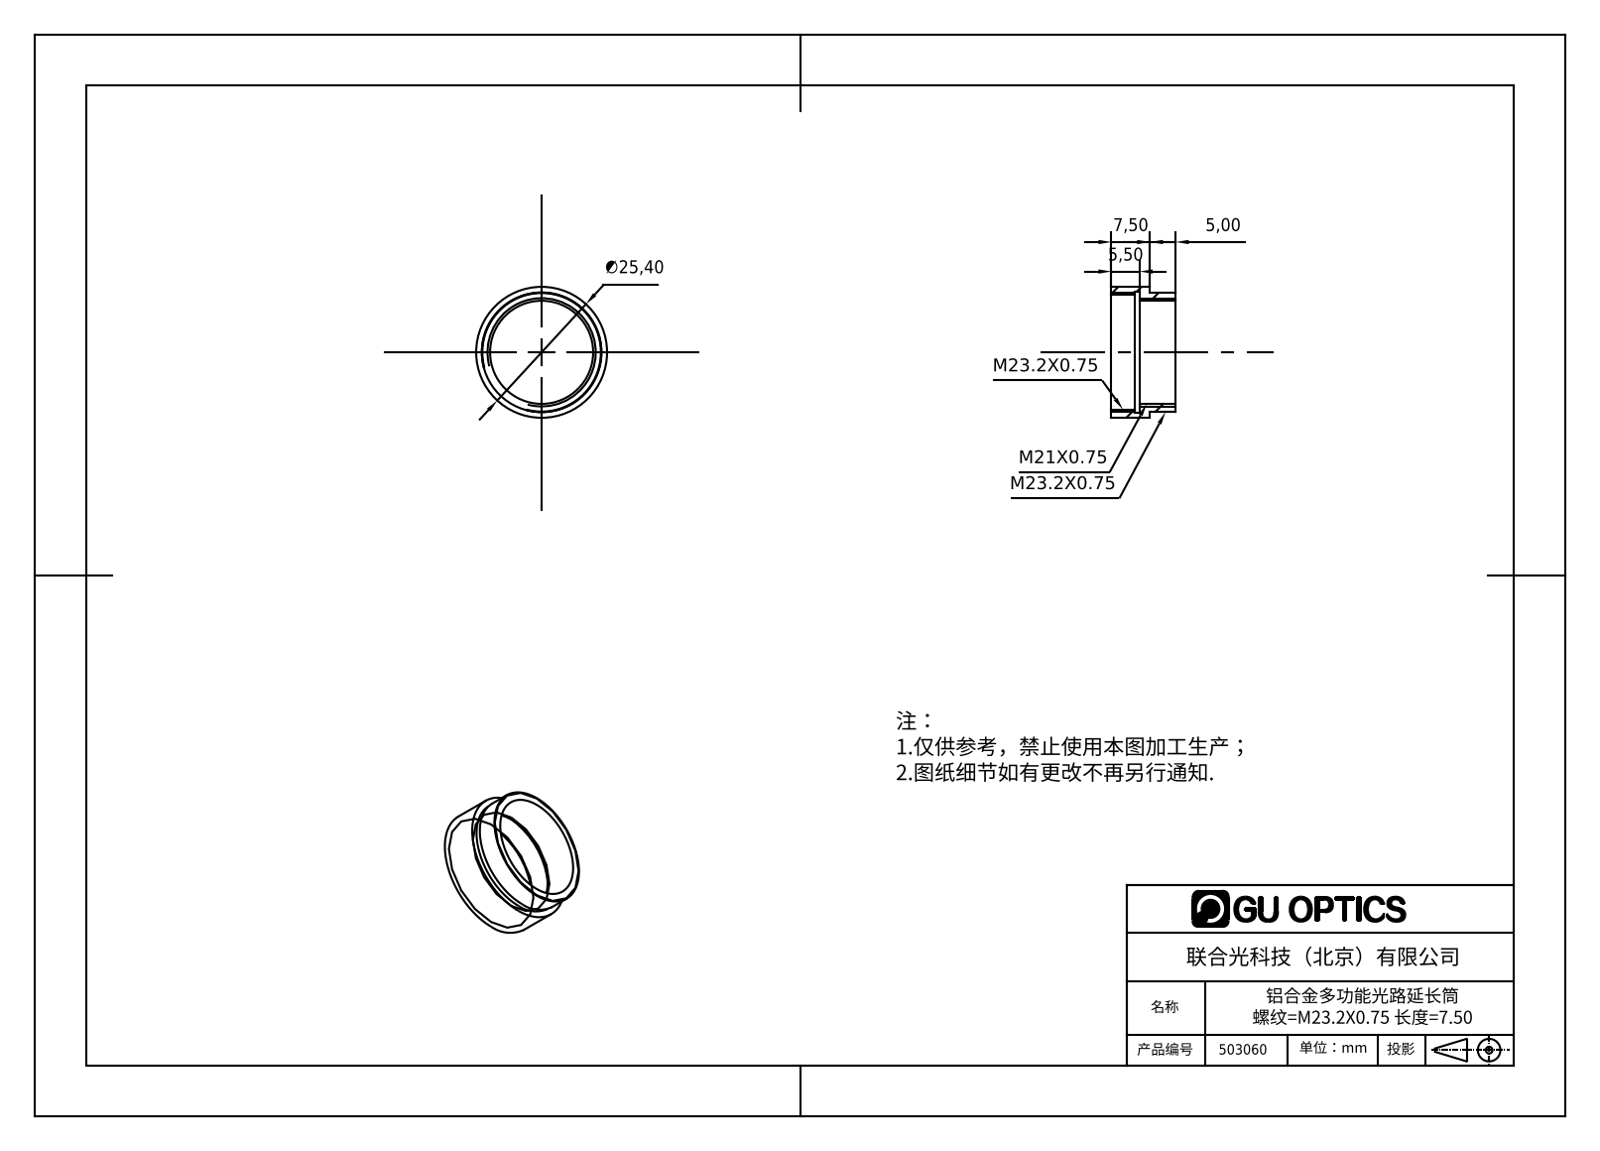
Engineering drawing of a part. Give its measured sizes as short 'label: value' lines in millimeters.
name: 503060
written by: SolidWorks 2016 (AUTOMOTIVE_DESIGN)
unit: mm
bodies: 1 solid, 18 faces (6 planar, 12 cylindrical, 0 other)
size: 25.4 × 25.4 × 12.5
volume: 1 536 mm³; area: 2 275 mm²
holes: 1× ⌀20, 1× ⌀22.2, 1× ⌀23.4
bosses: 1× ⌀25.4, 1× ⌀23.2, 1× ⌀23
face distances: 5.5, 12.5, 7, 7.5, 2, 5, 1, 3, 4.5, 8
